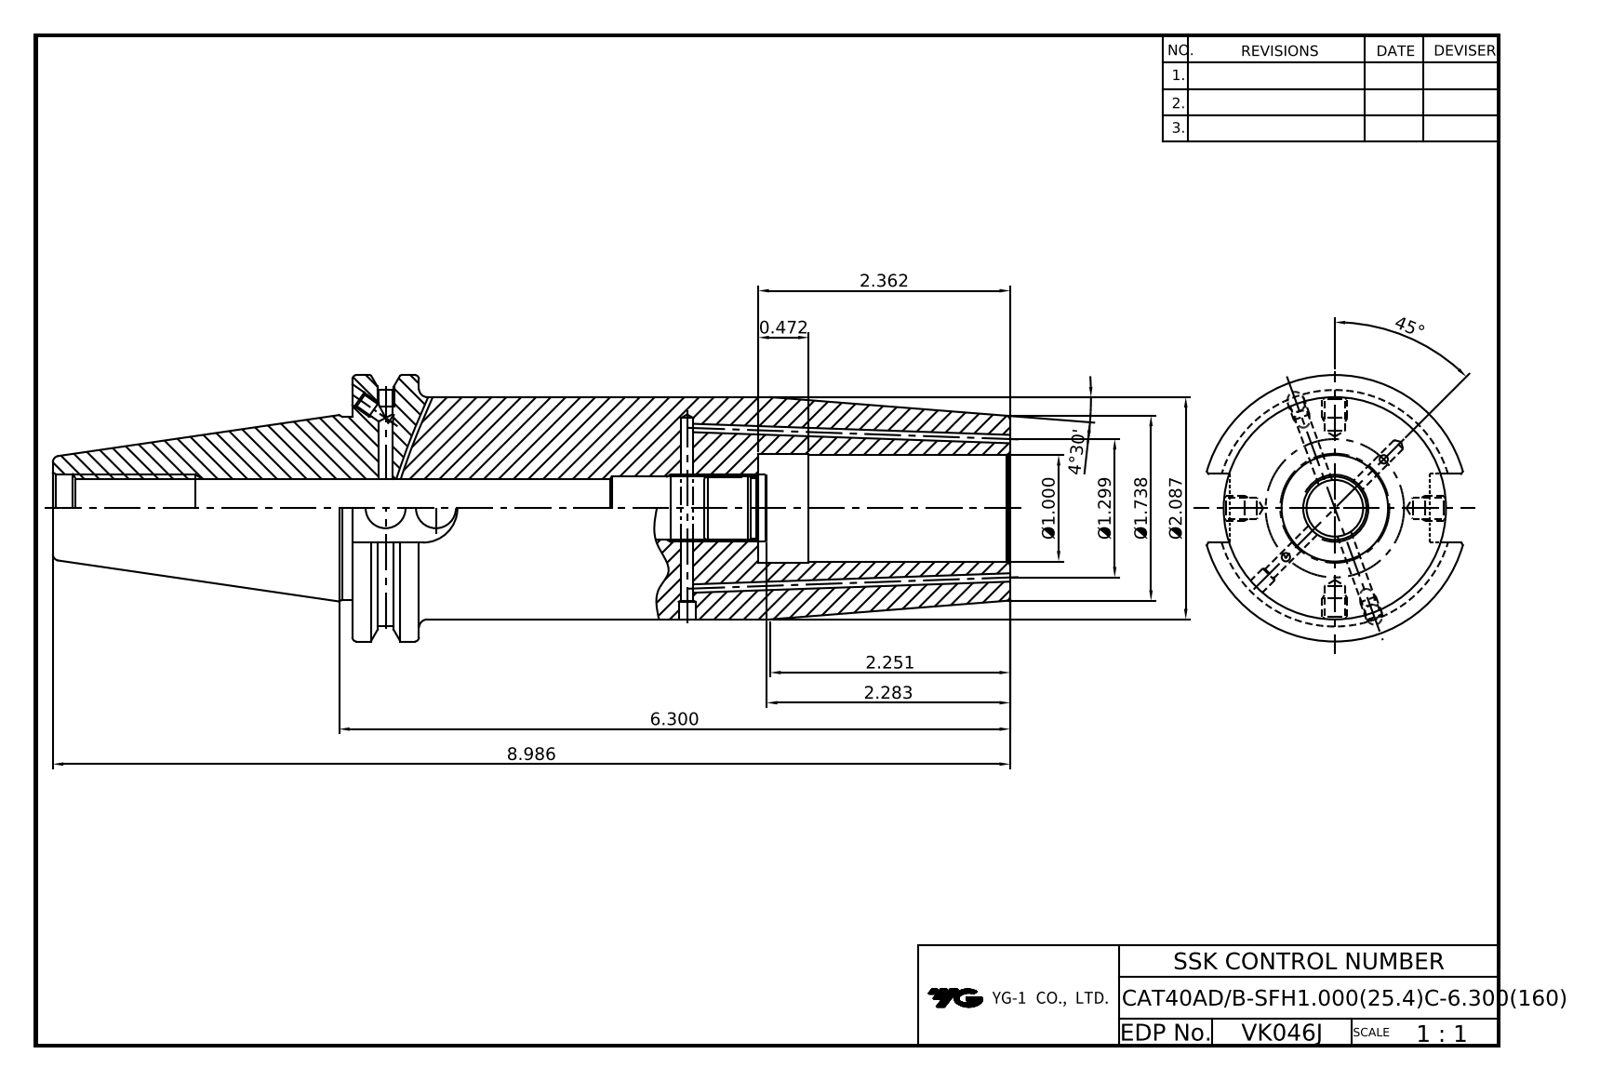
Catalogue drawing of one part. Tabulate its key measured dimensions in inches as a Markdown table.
| quantity | value |
| --- | --- |
| part name | LO-CAT40ADB-SFH25.4C-160 |
| STEP written by | Autodesk Inventor 2025 (AUTOMOTIVE_DESIGN) |
| units | inches |
| bodies | 1 solid, 89 faces (34 planar, 32 cylindrical, 23 other) |
| overall size | 8.986 × 2.5 × 2.405 |
| volume | 21.14 in³ |
| surface area | 80.77 in² |
| round holes (diameter × count) | 0.128 × 4, 0.098 × 2, 0.157 × 2, 0.165 × 2, 0.375 × 1, 0.527 × 1, 0.587 × 1, 0.642 × 1, 1 × 1, 1.047 × 1 |
| round bosses / shafts (diameter × count) | 2.5 × 1, 2.087 × 1, 1.717 × 1 |
| partial cylindrical surfaces (radius × count) | 0.322 × 1, 1.108 × 1 |
| main face-to-face distances | 6.174, 3.812, 2.362, 0.625, 3.187, 5.549, 1.874, 0.645, 2.812, 3.437 |
